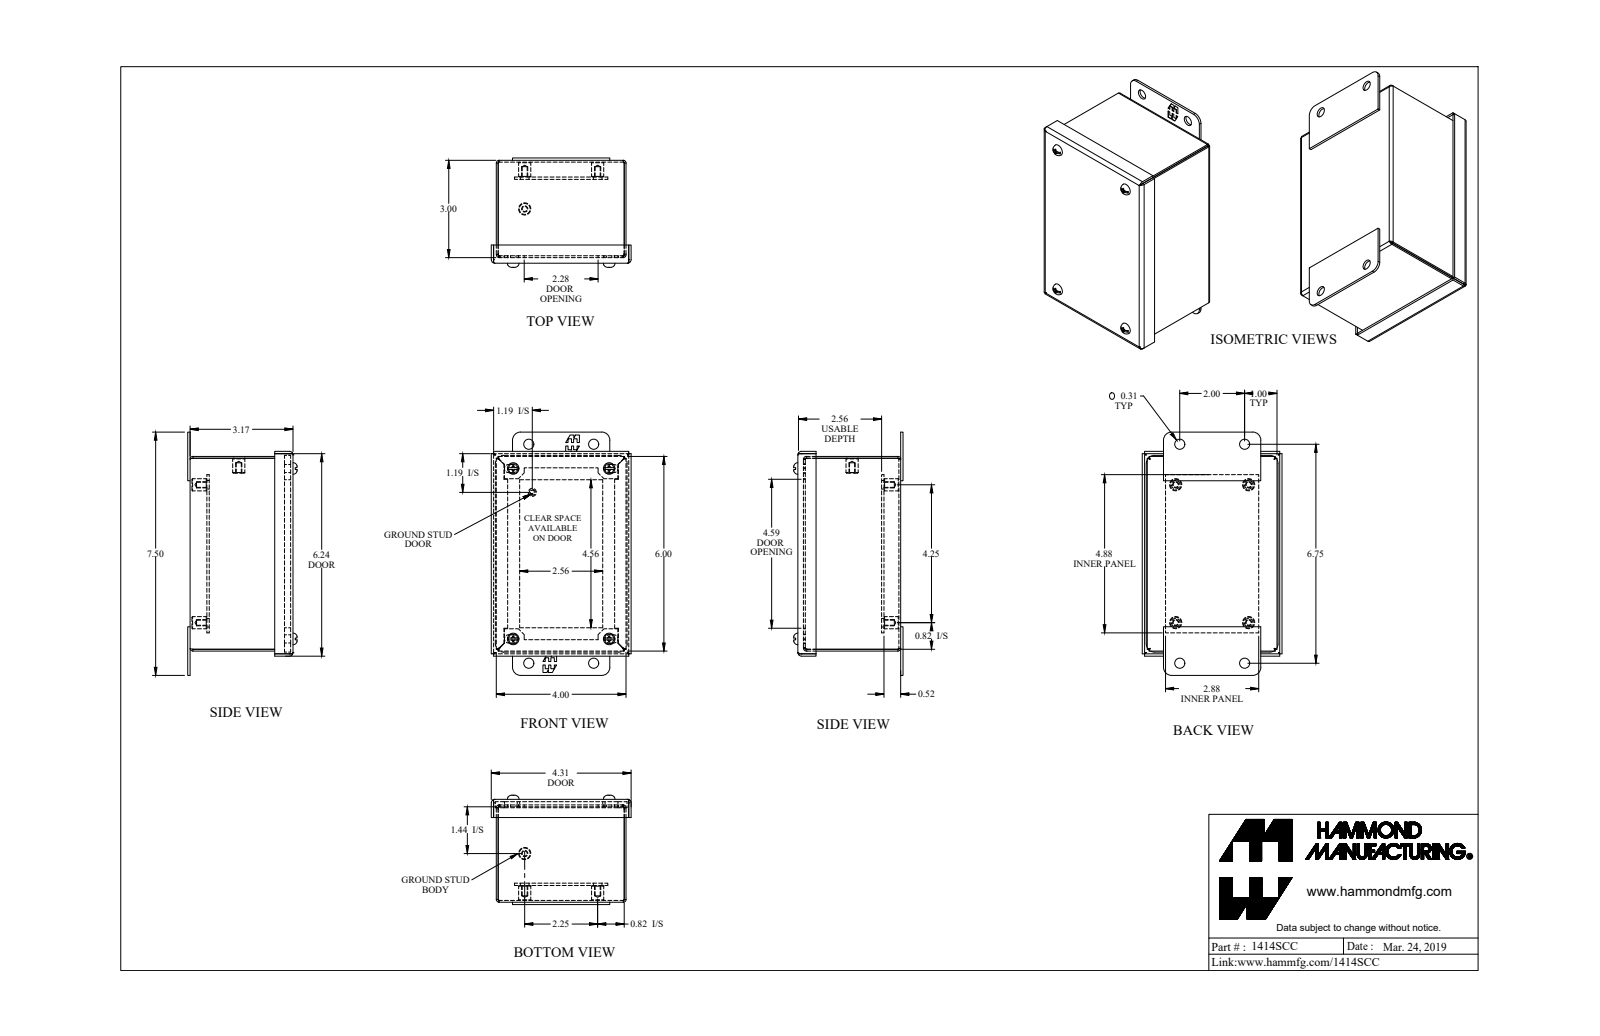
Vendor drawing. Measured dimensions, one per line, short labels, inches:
name: 1414SCC
written by: SolidWorks 2018 (AUTOMOTIVE_DESIGN)
unit: in
bodies: 24 solids, 560 faces (368 planar, 136 cylindrical, 56 other)
size: 7.5 × 4.312 × 3.371
volume: 12 in³; area: 345 in²
holes: 5× ⌀0.156, 4× ⌀0.159, 4× ⌀0.25, 4× ⌀0.265, 4× ⌀0.313
bosses: 5× ⌀0.375, 4× ⌀0.39, 4× ⌀0.275, 4× ⌀0.19, 4× ⌀0.148, 1× ⌀0.25, 1× ⌀0.188
rounds: 10× R0.188, 8× R0.029, 8× R0.086, 8× R0.125, 8× R0.25, 4× R0.007, 4× R0.046, 4× R0.079
face distances: 0.057, 0.072, 3.172, 3.943, 3.1, 2.583, 3.115, 3.043, 0.589, 5.943
hole spacings: 0.614, 1.257, 4.764, 4.809, 5.418, 5.502, 2.652, 2.653
